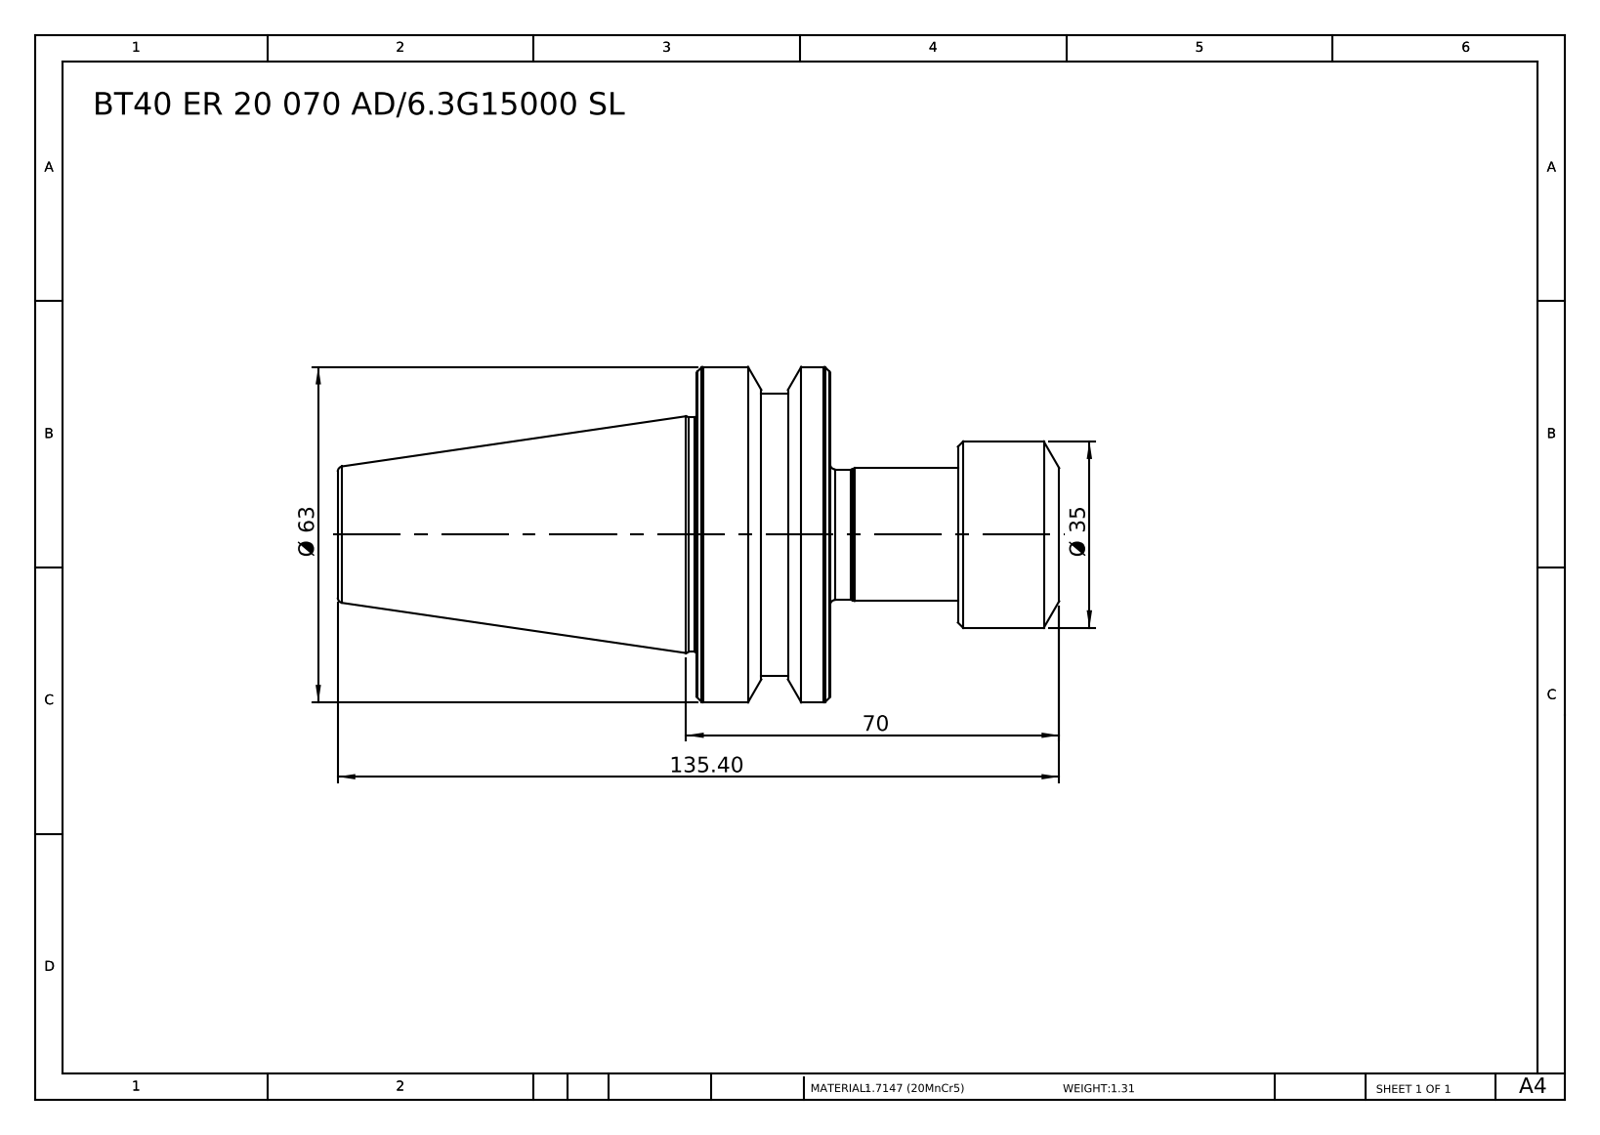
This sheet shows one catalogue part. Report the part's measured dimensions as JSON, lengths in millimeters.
{"part_name": "BT40 ER 20 070 AD-6.3G15000 SL", "step_written_by": "SolidWorks 2014 (CONFIG_CONTROL_DESIGN)", "units": "millimeters", "bodies": {"solids": 1, "faces": 55, "planar": 7, "cylindrical": 14, "other": 34}, "overall_size": [135.4, 63, 63], "volume_mm3": 167484, "surface_area_mm2": 22907, "round_bosses_or_shafts": [[63, 1], [53, 1], [44, 1], [35, 1], [24.9, 1], [24.5, 1]], "face_to_face_distances": [25, 43, 68, 135.4, 92.4, 67.4, 19, 24, 49, 116.4]}
